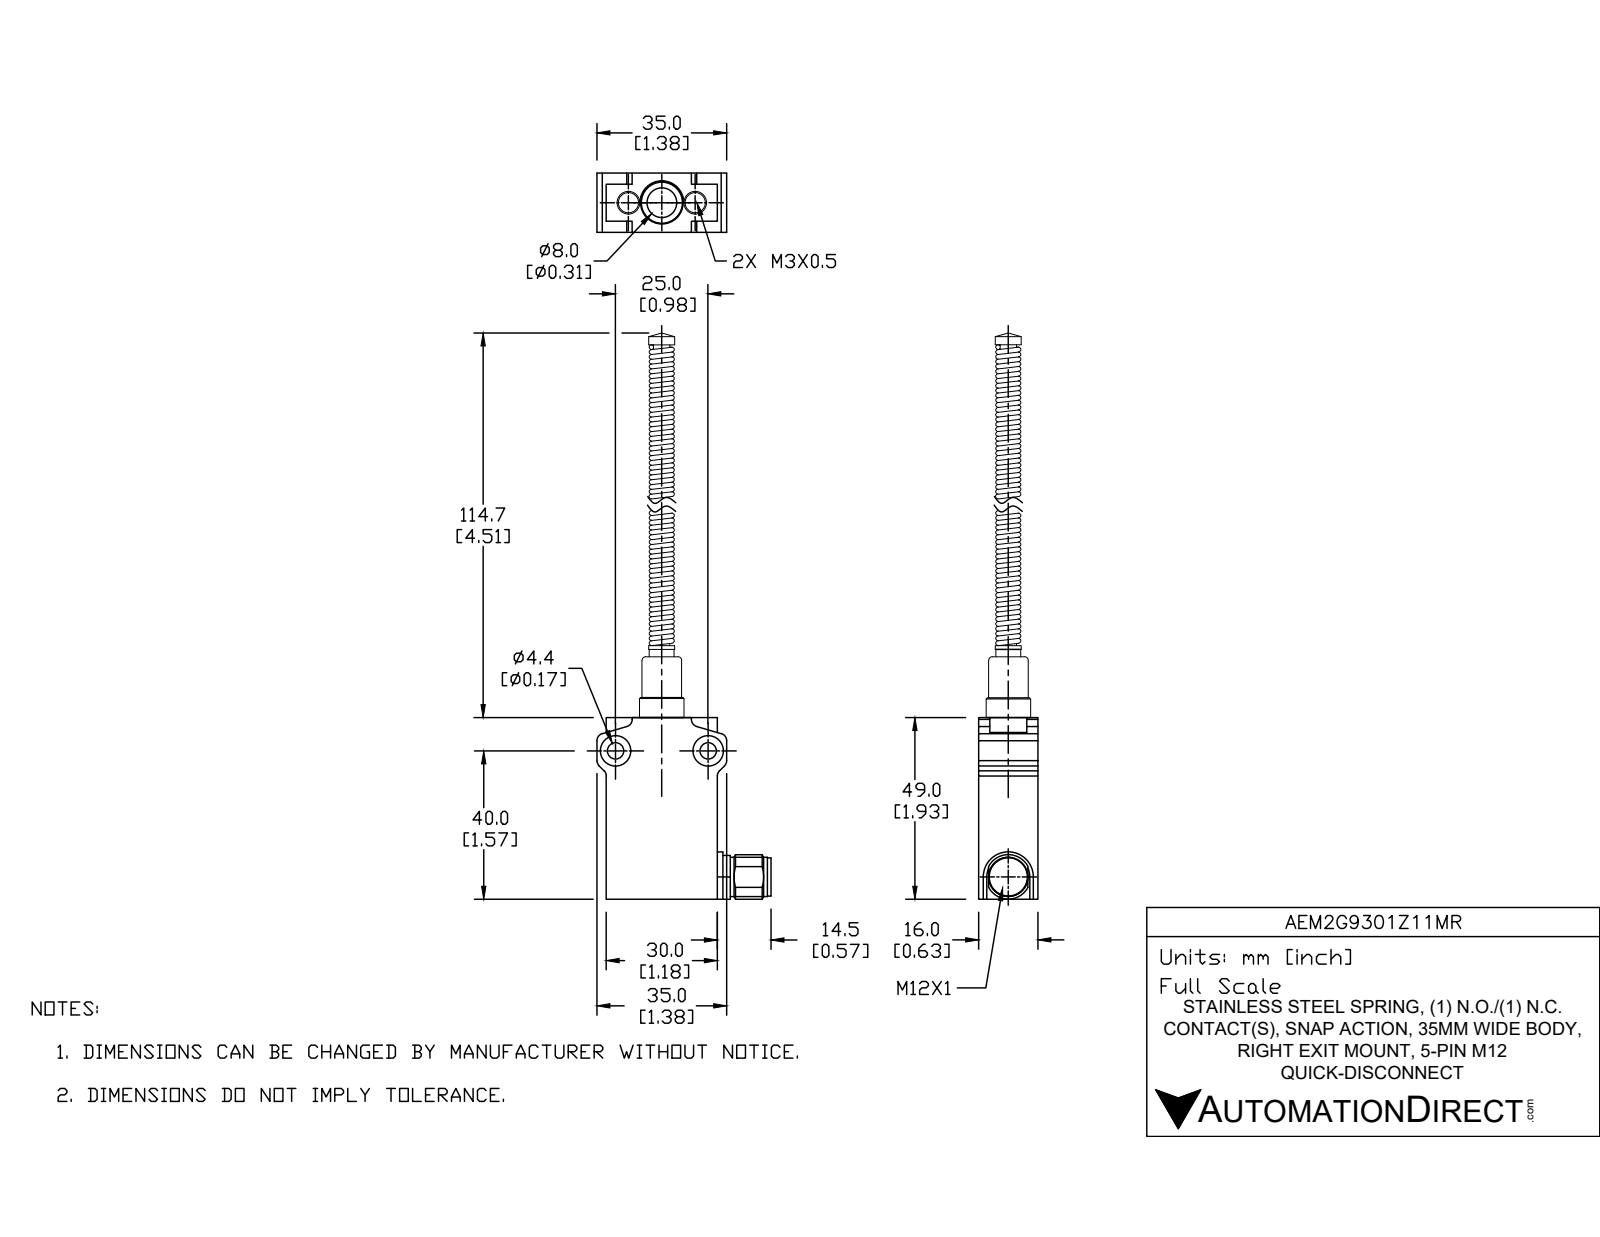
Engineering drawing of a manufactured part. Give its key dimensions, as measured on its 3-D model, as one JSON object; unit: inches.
{"part_name": "AEM2G9301Z11MR", "step_written_by": "SolidWorks 2019 (AUTOMOTIVE_DESIGN)", "units": "inches", "bodies": {"solids": 5, "faces": 270, "planar": 56, "cylindrical": 49, "other": 165}, "overall_size": [6.417, 1.831, 0.63], "volume_in3": 1.873, "surface_area_in2": 18.08, "round_holes": [[0.118, 2], [0.173, 2], [0.323, 2]], "round_bosses_or_shafts": [[0.472, 2], [0.433, 1], [0.417, 1], [0.406, 1], [0.276, 1], [0.197, 1]], "partial_cylinders_radius": [[0.079, 8], [0.256, 1]], "face_to_face_distances": [0.63, 1.181, 2.047, 0.472, 1.858, 0.189, 0.098, 1.28, 0.157, 0.118], "hole_center_spacings": [0.748, 0.984]}
